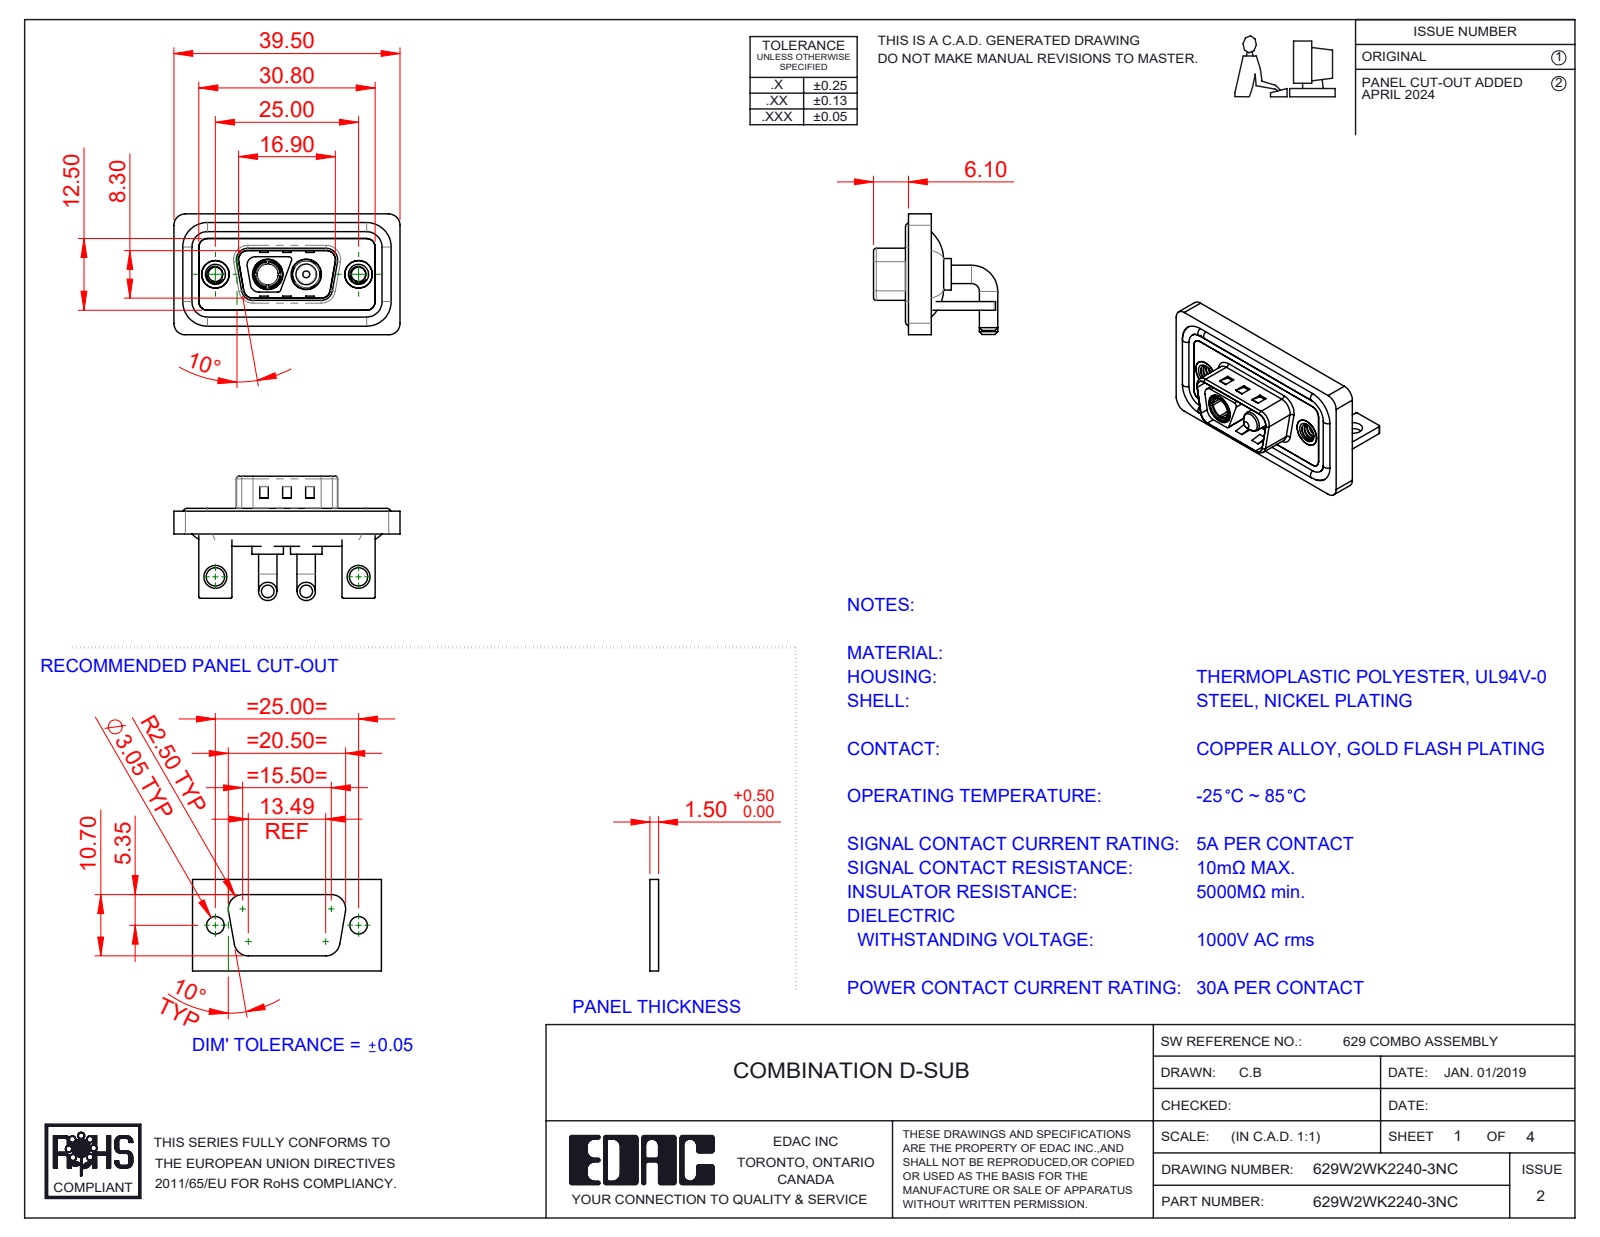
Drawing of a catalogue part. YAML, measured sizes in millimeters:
part_name: "629Combo Stabilizer Bracket; 629Combo Shell Rear_09 Contacts; 629Combo Housing_2WK2; 629W2WK2240-3NC (+5 more)"
step_written_by: "SolidWorks 2023 (CONFIG_CONTROL_DESIGN)"
units: millimeters
bodies: {solids: 13, faces: 580, planar: 209, cylindrical: 249, other: 122}
overall_size: [39.5, 21.7, 21.1]
volume: 5012
surface_area: 8158
round_holes:
  - {diameter: 2.5, count: 2}
  - {diameter: 3.2, count: 2}
  - {diameter: 4, count: 2}
  - {diameter: 4.8, count: 2}
  - {diameter: 4.85, count: 2}
  - {diameter: 5, count: 2}
  - {diameter: 5.3, count: 2}
  - {diameter: 3.7, count: 1}
round_bosses_or_shafts:
  - {diameter: 3.2, count: 4}
  - {diameter: 1.6, count: 4}
  - {diameter: 5.5, count: 2}
  - {diameter: 5.2, count: 2}
  - {diameter: 4.9, count: 2}
  - {diameter: 4.75, count: 2}
  - {diameter: 3.75, count: 2}
  - {diameter: 4.96, count: 1}
partial_cylinders:
  - {radius: 1.5, count: 20}
  - {radius: 2, count: 19}
  - {radius: 0.25, count: 16}
  - {radius: 0.5, count: 11}
  - {radius: 1.6, count: 8}
  - {radius: 0.6, count: 4}
  - {radius: 0.65, count: 4}
  - {radius: 0.9, count: 4}
face_to_face_distances: [0.4, 1.5, 2.9, 0.8, 1.1, 1.2, 2.1, 1.6, 3.7, 2.5]
hole_center_spacings: [9.14, 15.86, 25, 6.72]
